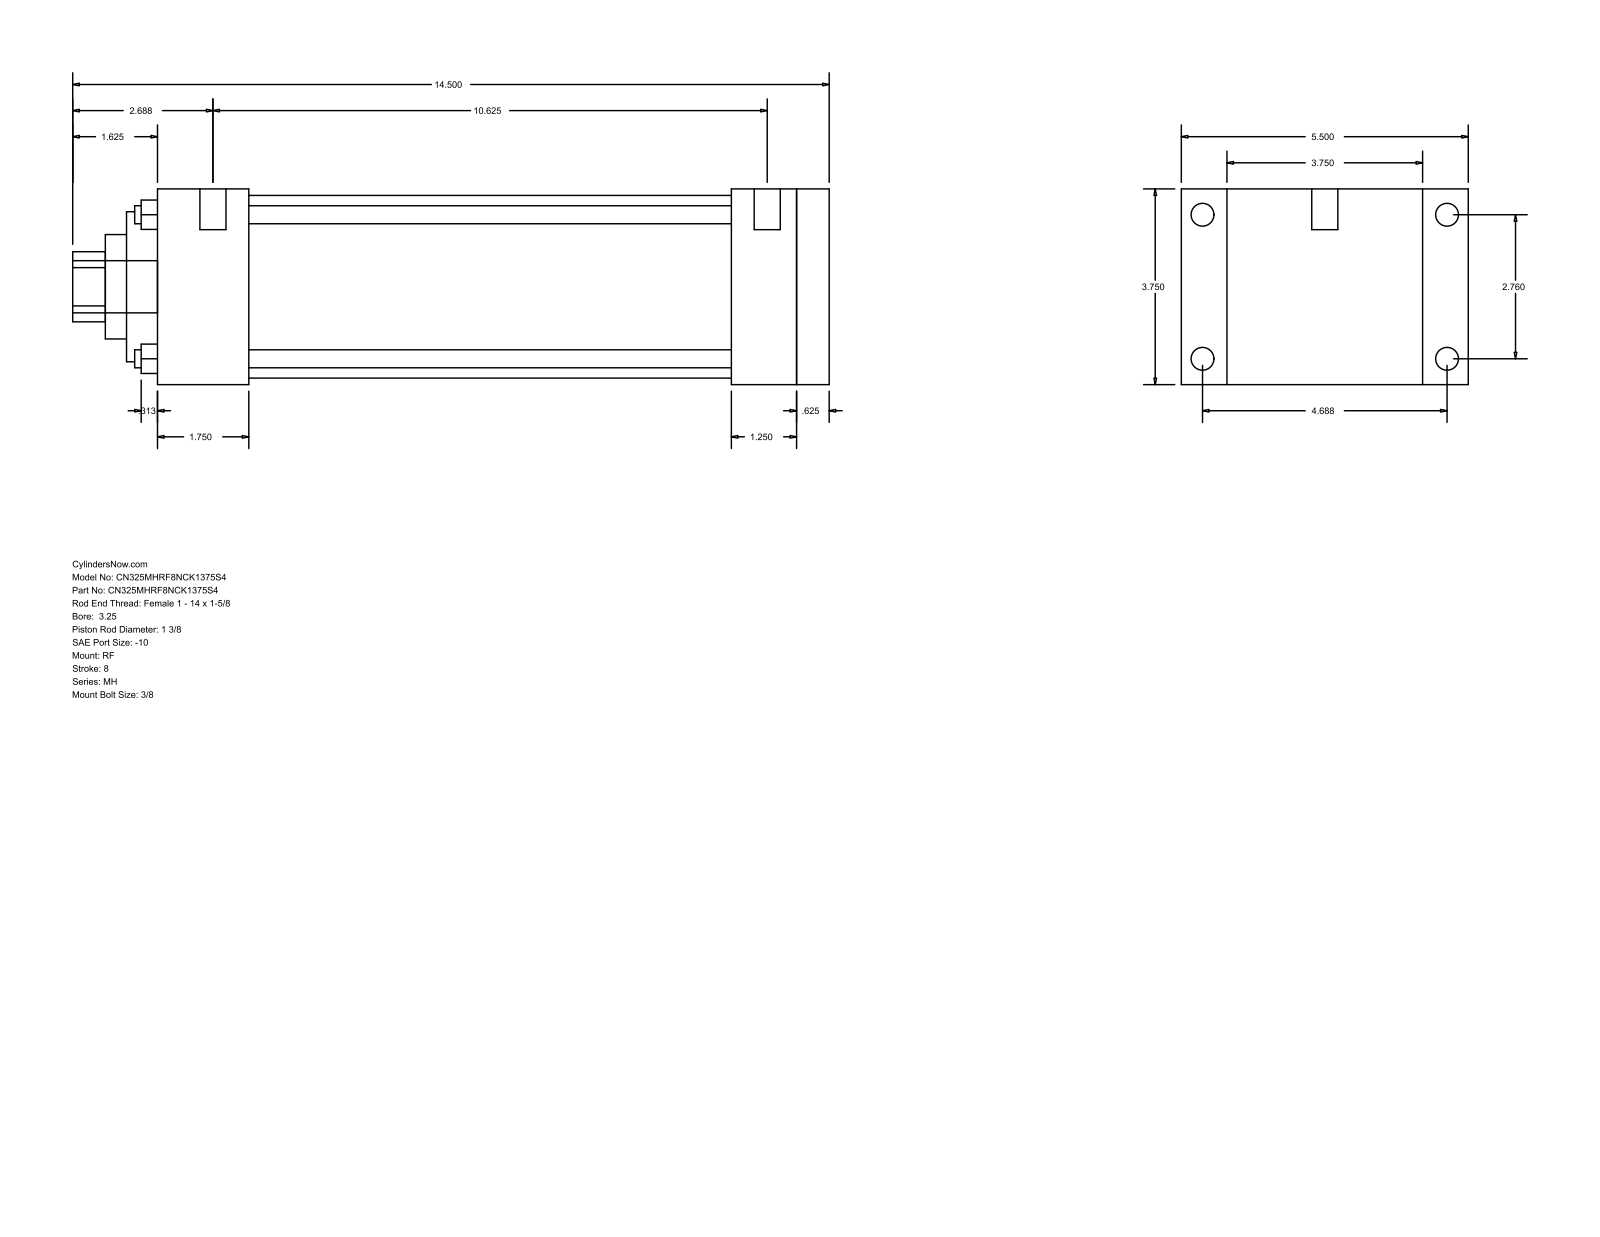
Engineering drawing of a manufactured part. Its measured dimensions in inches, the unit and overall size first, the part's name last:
Units: inches
Overall size (bounding box): 14.5 × 5.5 × 3.75
Round holes (diameter × count): ⌀0.345 ×4, ⌀1.375 ×1, ⌀2 ×1, ⌀2.875 ×1, ⌀3.5 ×1
Round bosses / shafts (diameter × count): ⌀0.438 ×4, ⌀0.219 ×4, ⌀0.5 ×2, ⌀1 ×1
Partial cylindrical surfaces — rounded edges, fillets, slot ends (radius × count): R0.672 ×1
Main face-to-face distances: 3.75, 12.875, 12.25, 0.625, 0.875, 4.625, 1.75, 10.5, 11.125, 11
Hole centre spacings: 1.952, 2.76, 3.903
Bodies: 0 solids, 94 faces (65 planar, 29 cylindrical, 0 other)
Part name (STEP PRODUCT): MH_RF__0325_1.375
STEP written by: GSSL Pune (CONFIG_CONTROL_DESIGN)
